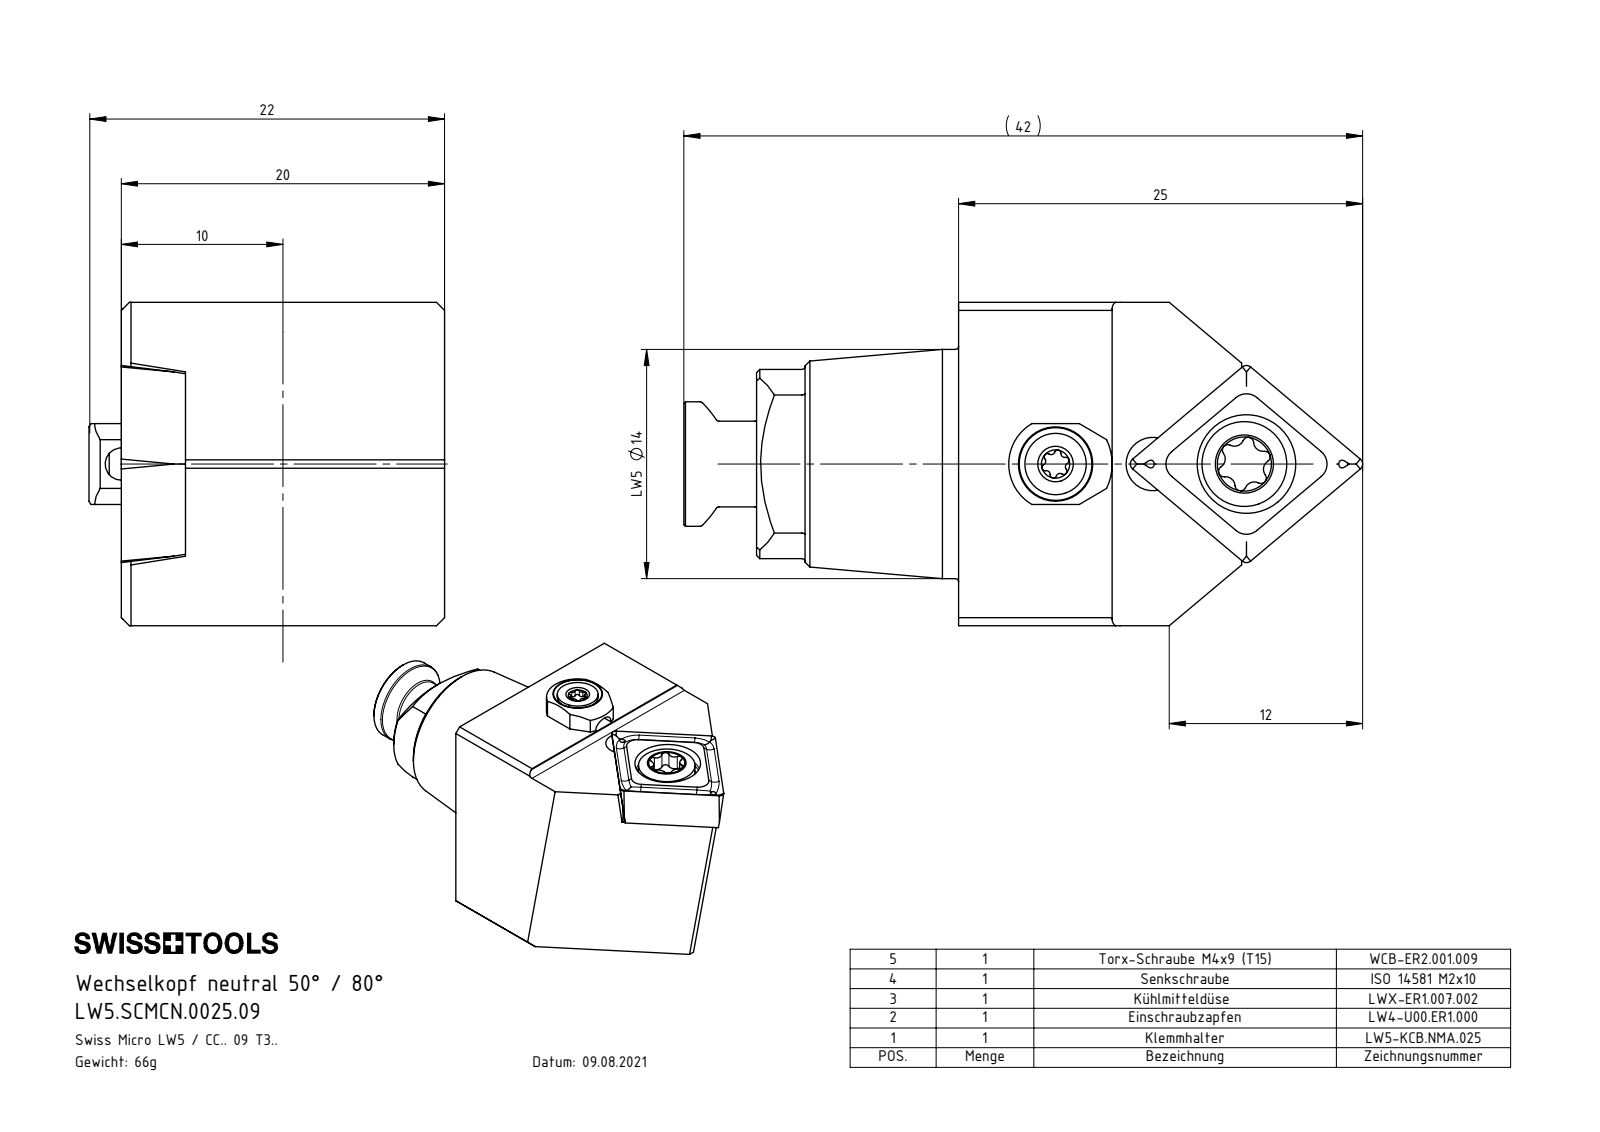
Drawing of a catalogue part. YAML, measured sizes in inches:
part_name: "LW5.SCMCN.0025.09; WCB-ER2.001.009_A; LW4-U00.ER1.000_D; CCMT09T304 (+3 more)"
step_written_by: "SolidWorks 2022 (CONFIG_CONTROL_DESIGN)"
units: inches
bodies: {solids: 6, faces: 262, planar: 69, cylindrical: 80, other: 113}
overall_size: [1.642, 0.866, 0.787]
volume: 0.512
surface_area: 6.398
round_holes:
  - {diameter: 0.079, count: 2}
  - {diameter: 0.13, count: 2}
  - {diameter: 0.063, count: 1}
  - {diameter: 0.098, count: 1}
  - {diameter: 0.118, count: 1}
  - {diameter: 0.173, count: 1}
  - {diameter: 0.217, count: 1}
  - {diameter: 0.24, count: 1}
round_bosses_or_shafts:
  - {diameter: 0.558, count: 1}
  - {diameter: 0.303, count: 1}
  - {diameter: 0.236, count: 1}
  - {diameter: 0.209, count: 1}
  - {diameter: 0.207, count: 1}
  - {diameter: 0.197, count: 1}
  - {diameter: 0.157, count: 1}
  - {diameter: 0.15, count: 1}
partial_cylinders:
  - {radius: 0.008, count: 8}
  - {radius: 0.009, count: 6}
  - {radius: 0.013, count: 6}
  - {radius: 0.023, count: 6}
  - {radius: 0.02, count: 1}
  - {radius: 0.039, count: 1}
  - {radius: 0.114, count: 1}
  - {radius: 0.138, count: 1}
face_to_face_distances: [0.787, 0.631, 0.156, 0.764, 0.133, 0.024, 0.492, 0.079, 0.118, 0.236]
hole_center_spacings: [0.221, 0.223, 0.228, 0.444, 0.449]
